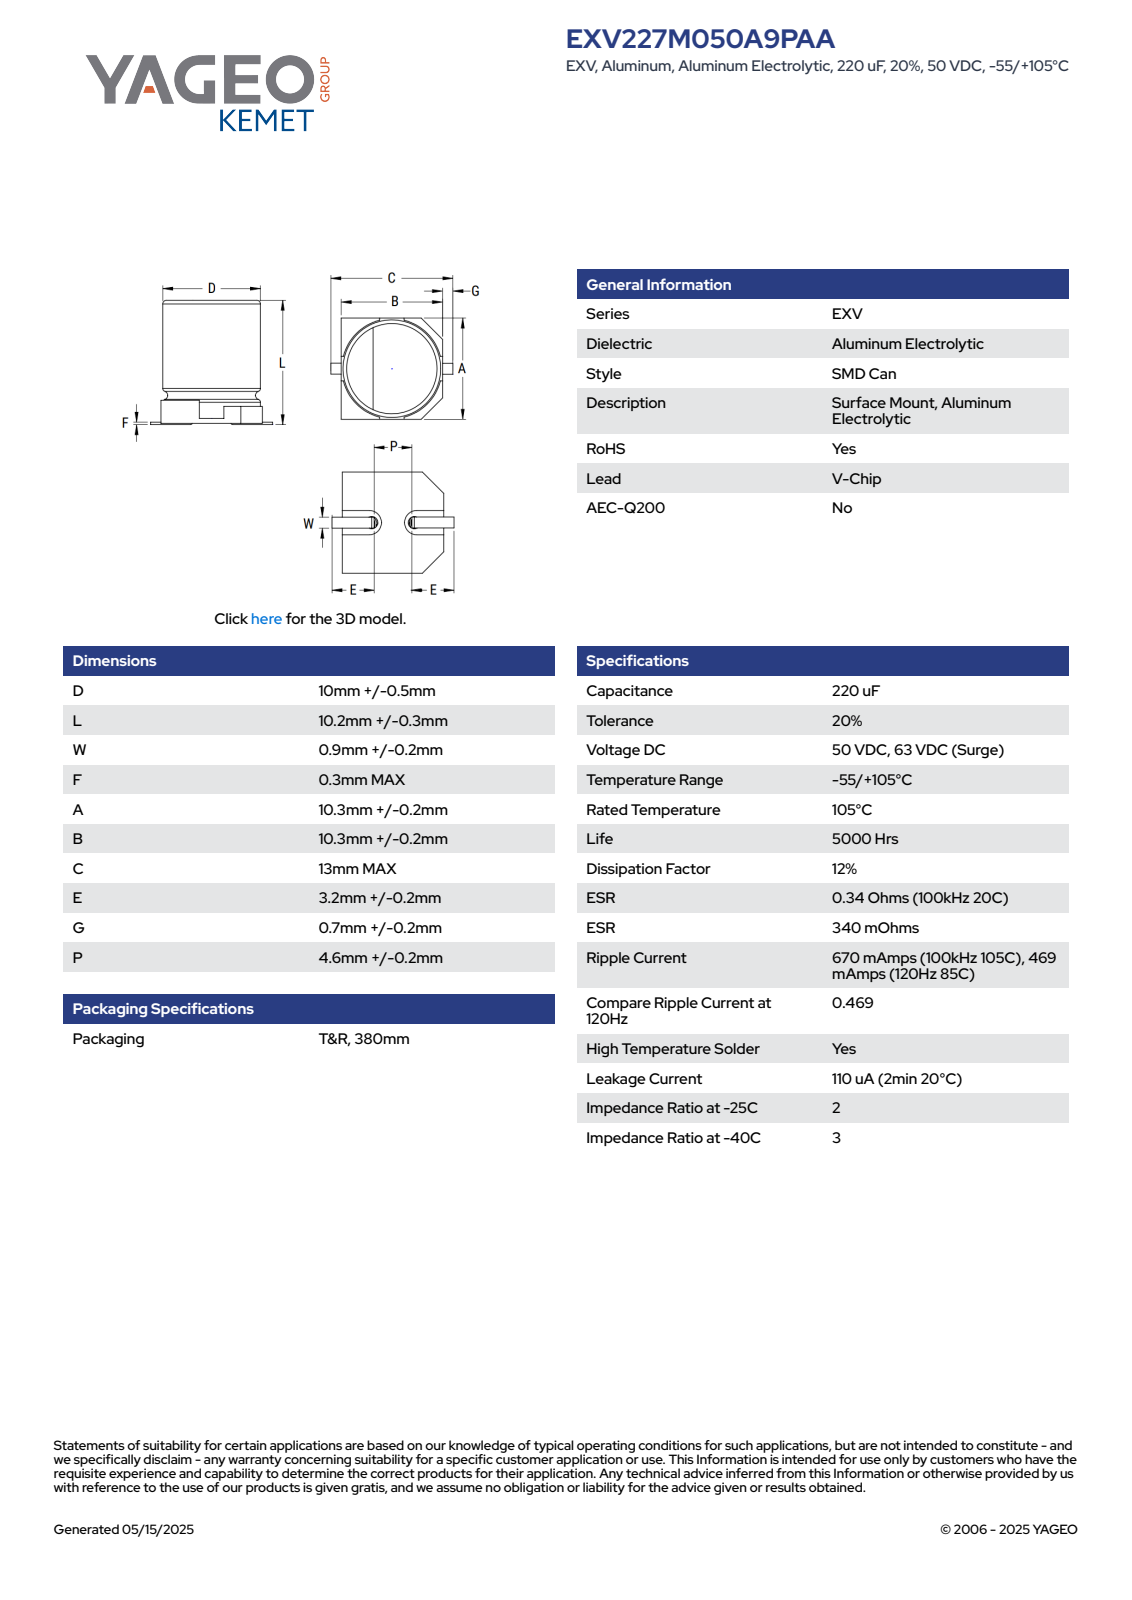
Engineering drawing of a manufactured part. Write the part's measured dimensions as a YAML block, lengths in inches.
part_name: "CAC_S_10X10.2_D10.5L10.5W1.1F0.3A10.5B10.5C13E3.7P4.8"
step_written_by: "SolidWorks 2021 (AUTOMOTIVE_DESIGN)"
units: inches
bodies: {solids: 5, faces: 78, planar: 61, cylindrical: 11, other: 6}
overall_size: [0.457, 0.414, 0.413]
volume: 0.051
surface_area: 1.23
round_bosses_or_shafts:
  - {diameter: 0.395, count: 1}
partial_cylinders:
  - {radius: 0.008, count: 2}
  - {radius: 0.164, count: 1}
  - {radius: 0.207, count: 1}
face_to_face_distances: [0.02, 0.402, 0.381, 0.413, 0.103, 0.083, 0.298, 0.032, 0.115, 0.069]
